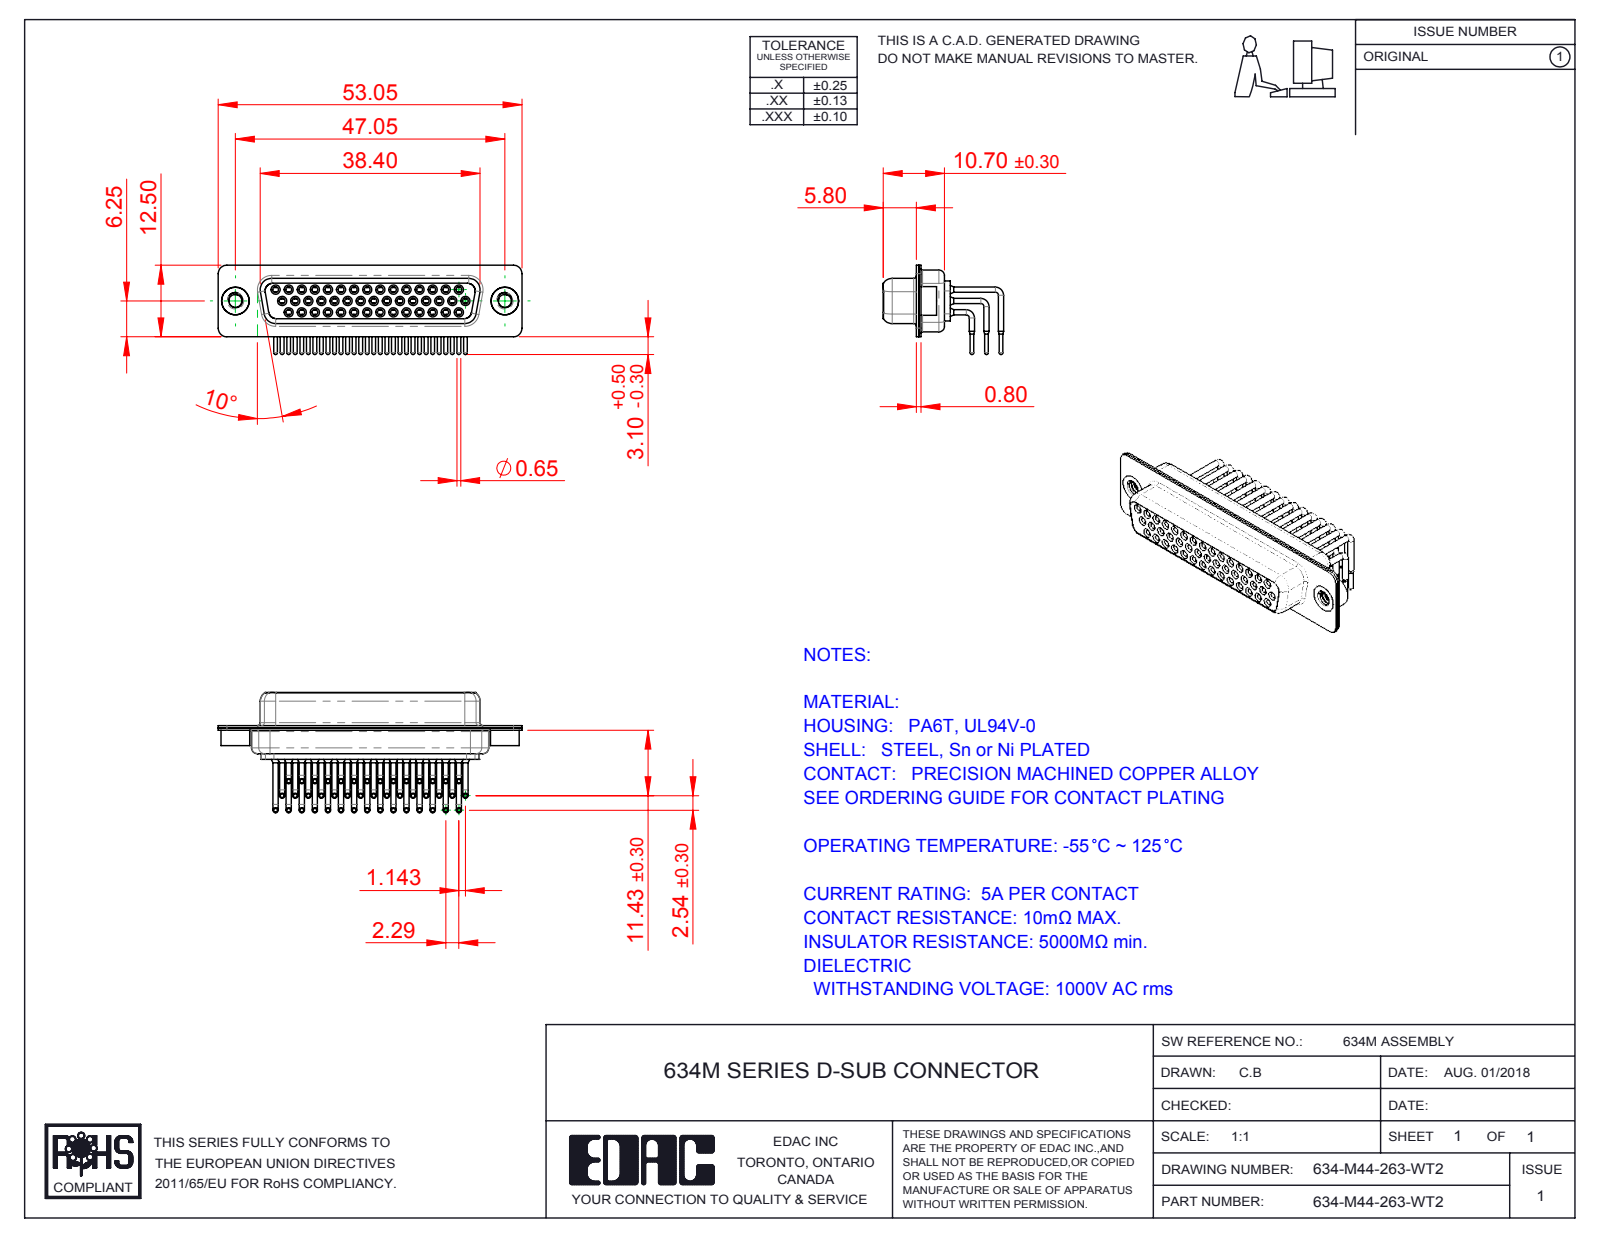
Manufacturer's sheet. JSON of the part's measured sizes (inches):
{"part_name": "634M Contact Row 1; 634M Contact Row 3; 634M Shell Front_44 Contacts; 634M Shell Rear_44 Contacts (+4 more)", "step_written_by": "SolidWorks 2016 (CONFIG_CONTROL_DESIGN)", "units": "inches", "bodies": {"solids": 49, "faces": 2611, "planar": 727, "cylindrical": 1149, "other": 735}, "overall_size": [2.089, 0.828, 0.614], "volume_in3": 0.234, "surface_area_in2": 20.21, "round_holes": [[0.039, 44], [0.043, 44], [0.067, 44], [0.071, 44], [0.079, 44], [0.089, 2], [0.157, 2], [0.189, 2]], "round_bosses_or_shafts": [[0.035, 88], [0.063, 44], [0.059, 44], [0.026, 44], [0.197, 2], [0.193, 2]], "partial_cylinders_radius": [[0.059, 16], [0.079, 12], [0.053, 8], [0.063, 8], [0.01, 4], [0.02, 4], [0.024, 4], [0.026, 4]], "face_to_face_distances": [0.016, 0.057, 0.352, 0.091, 0.075, 0.335, 0.244, 0.278, 0.018, 0.033], "hole_center_spacings": [0.09, 0.156, 0.09, 0.18, 0.324, 0.27, 0.45, 0.413]}
